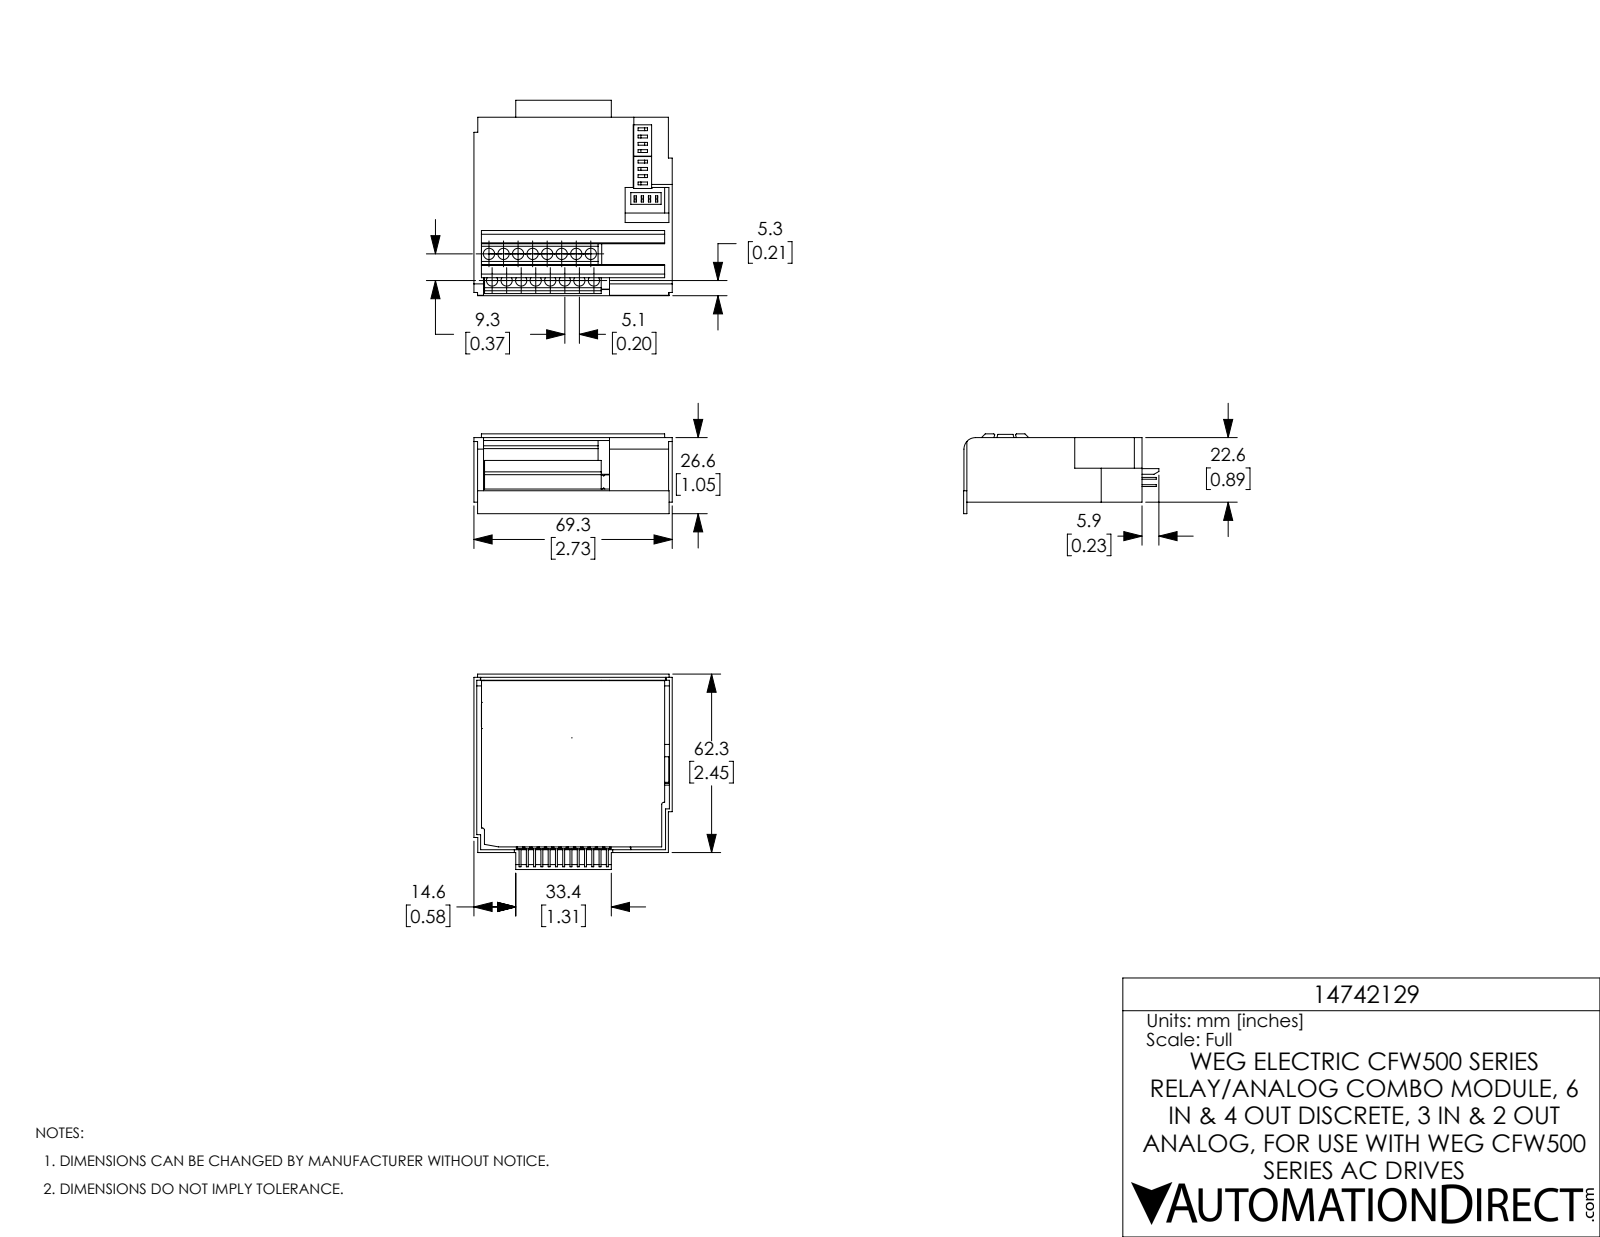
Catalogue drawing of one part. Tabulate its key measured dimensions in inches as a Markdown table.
| quantity | value |
| --- | --- |
| part name | 14742129_MODULO IO CFW500_IOAD Coord nc |
| STEP written by | SolidWorks 2017 (AUTOMOTIVE_DESIGN) |
| units | inches |
| bodies | 2 solids, 529 faces (491 planar, 38 cylindrical, 0 other) |
| overall size | 2.726 × 2.685 × 1.096 |
| volume | 1.606 in³ |
| surface area | 47.17 in² |
| round holes (diameter × count) | 0.154 × 8, 0.155 × 8 |
| partial cylindrical surfaces (radius × count) | 0.03 × 2, 0.118 × 1, 0.157 × 1 |
| main face-to-face distances | 0.039, 0.063, 0.73, 0.667, 0.707, 0.77, 2.687, 2.727, 0.051, 2.369 |
| hole center spacings | 0.2, 0.4, 0.6, 0.369, 0.8, 0.399, 0.44, 0.512 |
